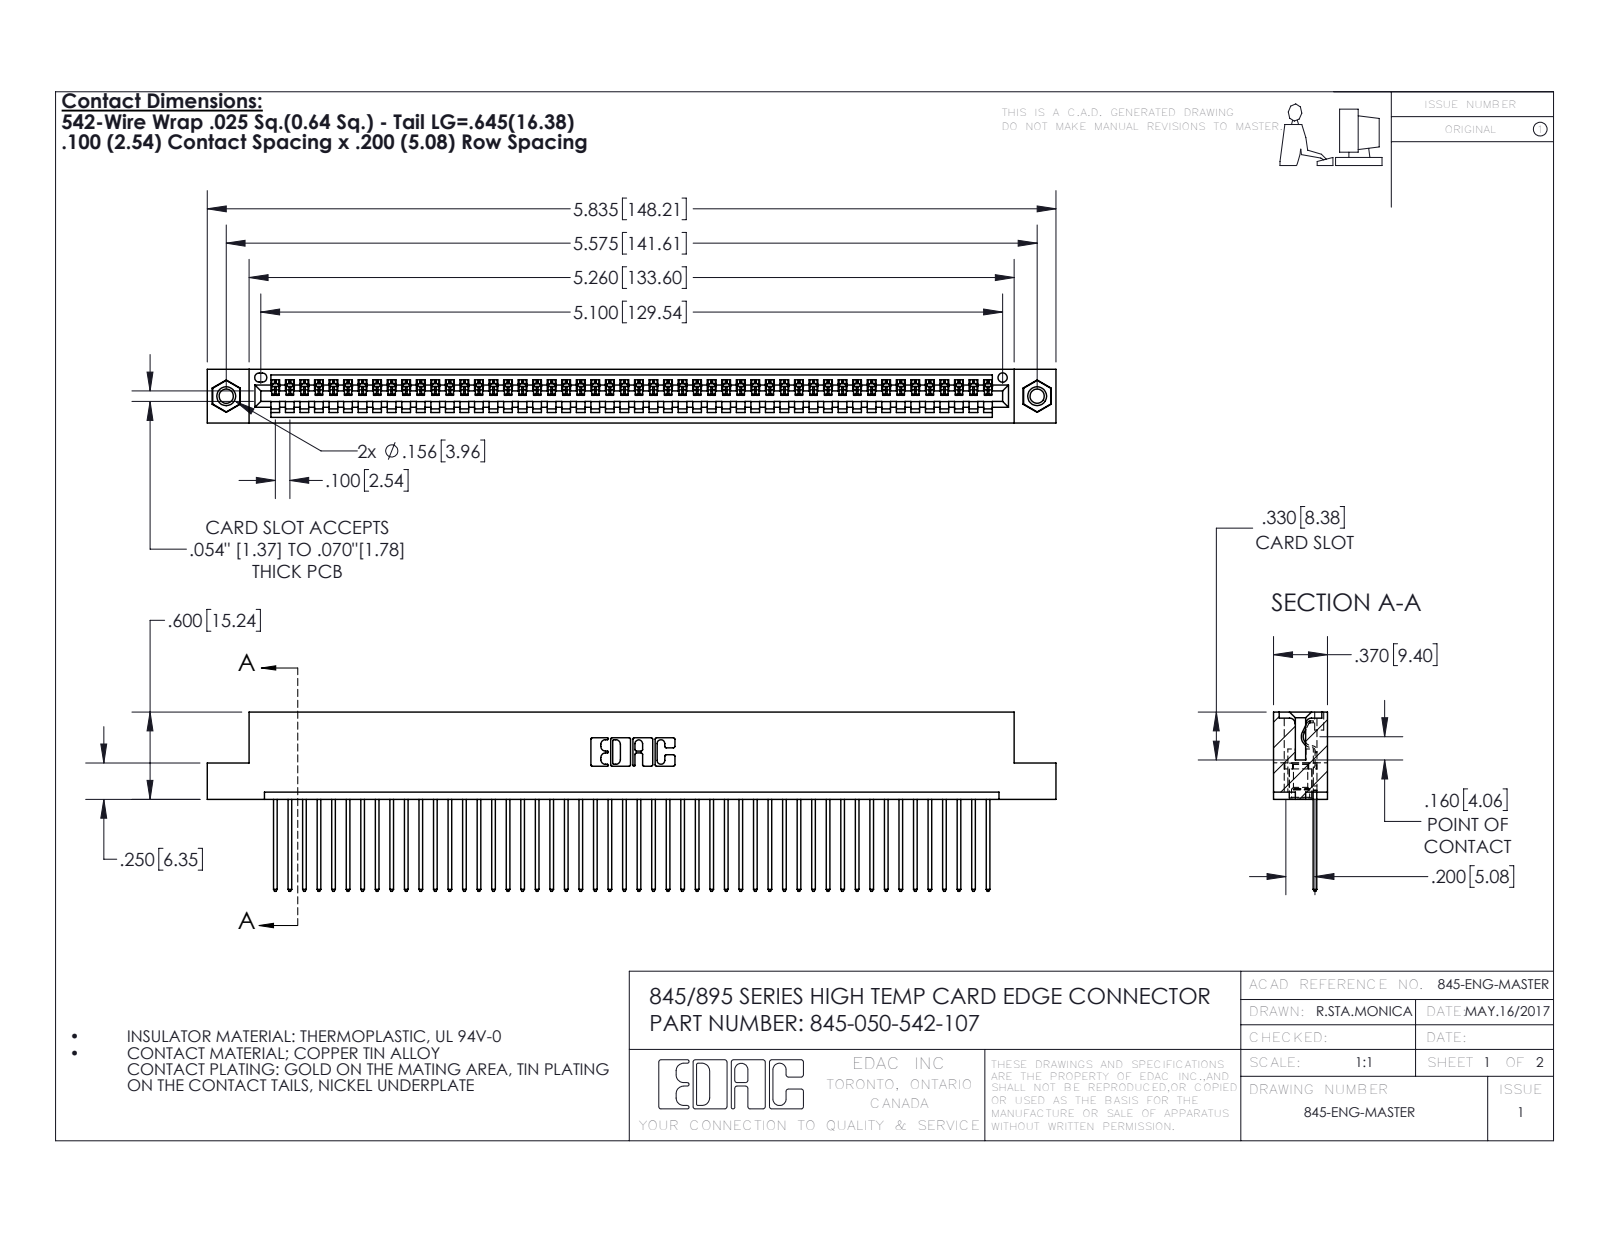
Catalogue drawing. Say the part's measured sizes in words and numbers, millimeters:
The part is named "345 Part_Flush Mounting Lugs - 0.156 Dia-TI; 345-292-001_345-293-142; 345-250-001_345-250-005-103; 345-050-542-107". Its 3-D file was written by "SolidWorks 2016 (CONFIG_CONTROL_DESIGN)". It is 53 solids with 3086 faces: 2112 planar, 958 cylindrical and 16 other. Overall it measures 148.2 by 31.3 by 9.4 millimeters. Its volume is 14 200 cubic millimeters and its surface area 19 770 square millimeters. Round holes: 2 of diameter 2.5, 2 of diameter 3.2, 2 of diameter 4, 1 of diameter 1.6. Round bosses or shafts: 2 of diameter 3.9. Partial cylindrical surfaces (rounded edges, fillets, slot ends): 100 of radius 0.2, 100 of radius 0.3, 22 of radius 0.3, 6 of radius 0.2, 6 of radius 0.8, 3 of radius 0.7, 2 of radius 0.8, 2 of radius 1. The main face-to-face distances are 1.8, 7.6, 2.5, 6.9, 0.6, 9.4, 5.1, 5.7, 3.8, 1.8. The hole center spacings are 6.9, 135.6, 141.6.
